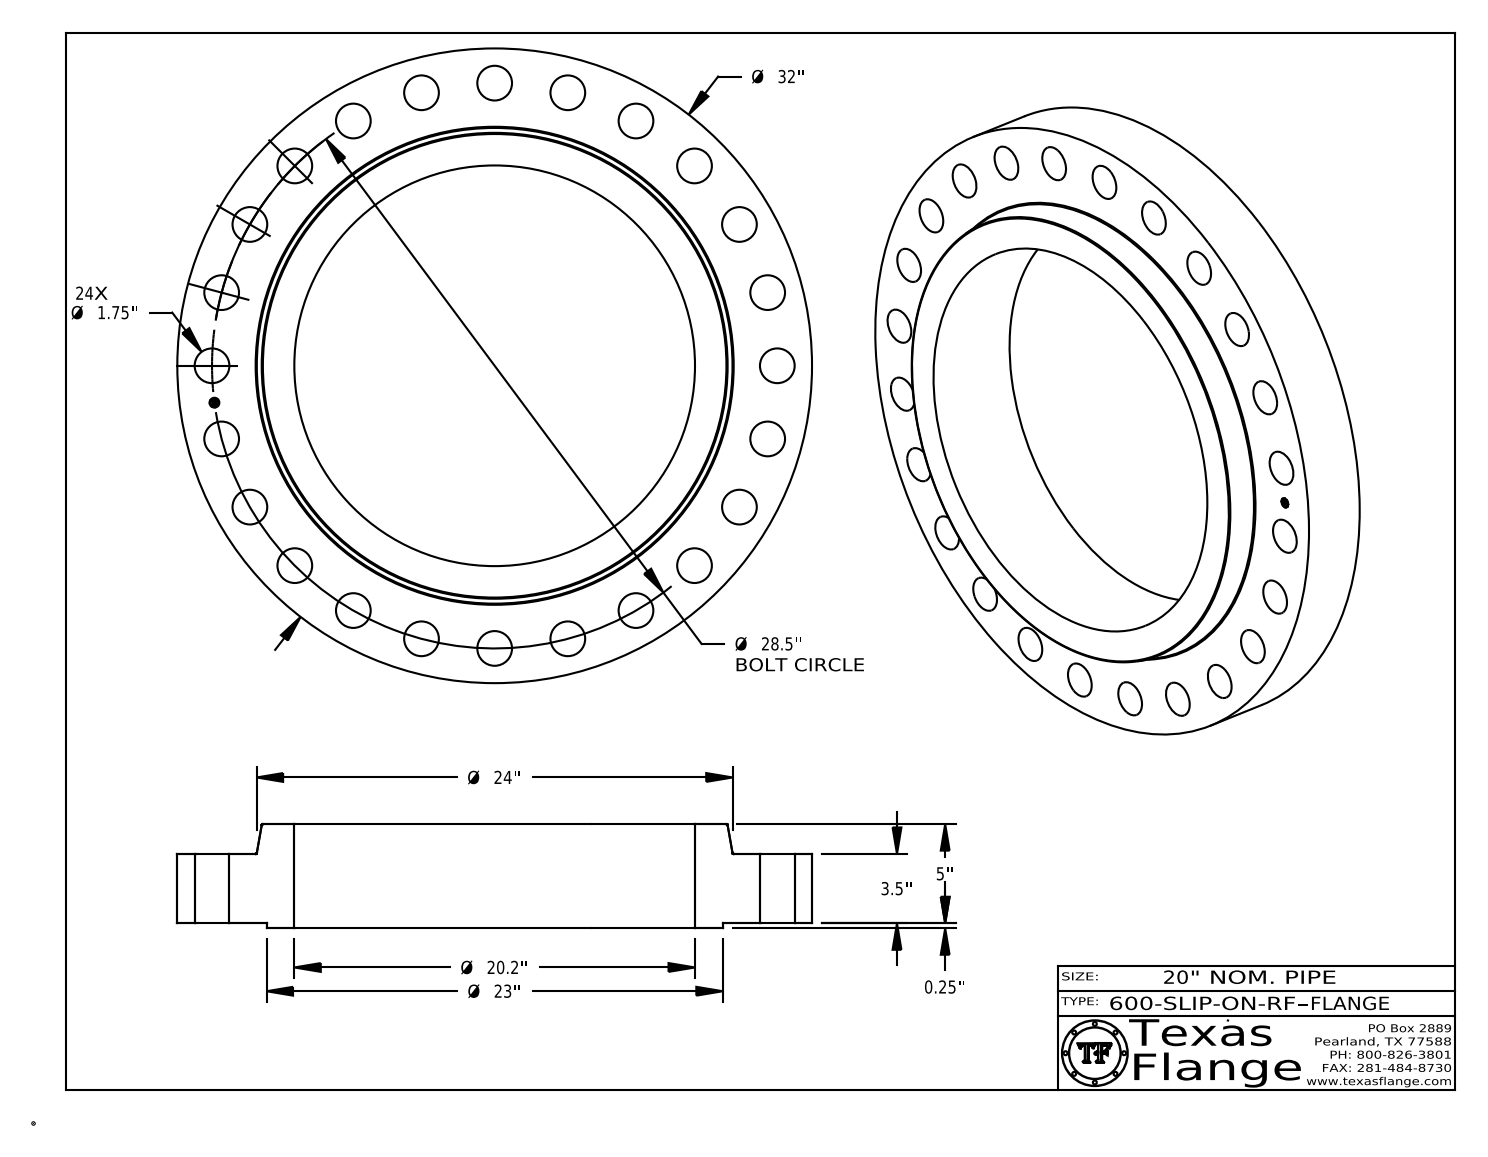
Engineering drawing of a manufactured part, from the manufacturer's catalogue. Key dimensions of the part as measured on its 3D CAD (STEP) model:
Part name (STEP PRODUCT): 600-SLIP-ON-RF
STEP written by: CATIA V5 STEP AP214 (AUTOMOTIVE_DESIGN)
Units: inches
Bodies: 1 solid, 449 faces (369 planar, 74 cylindrical, 6 other)
Overall size (bounding box): 32 × 32 × 5.25
Volume: 1 698 in³ · Surface area: 2 108 in²
Round holes (diameter × count): ⌀1.75 ×24, ⌀0.495 ×1, ⌀20.2 ×1
Round bosses / shafts (diameter × count): ⌀0.03 ×8, ⌀32 ×1, ⌀23 ×1, ⌀0.39 ×1
Main face-to-face distances: 3.5, 5, 1.5, 0.25, 3.75, 5.25, 0.015, 3.735, 3.485, 1.515
Hole centre spacings: 14.25, 3.72, 7.376, 24.682, 26.331, 27.529, 20.153, 10.907
